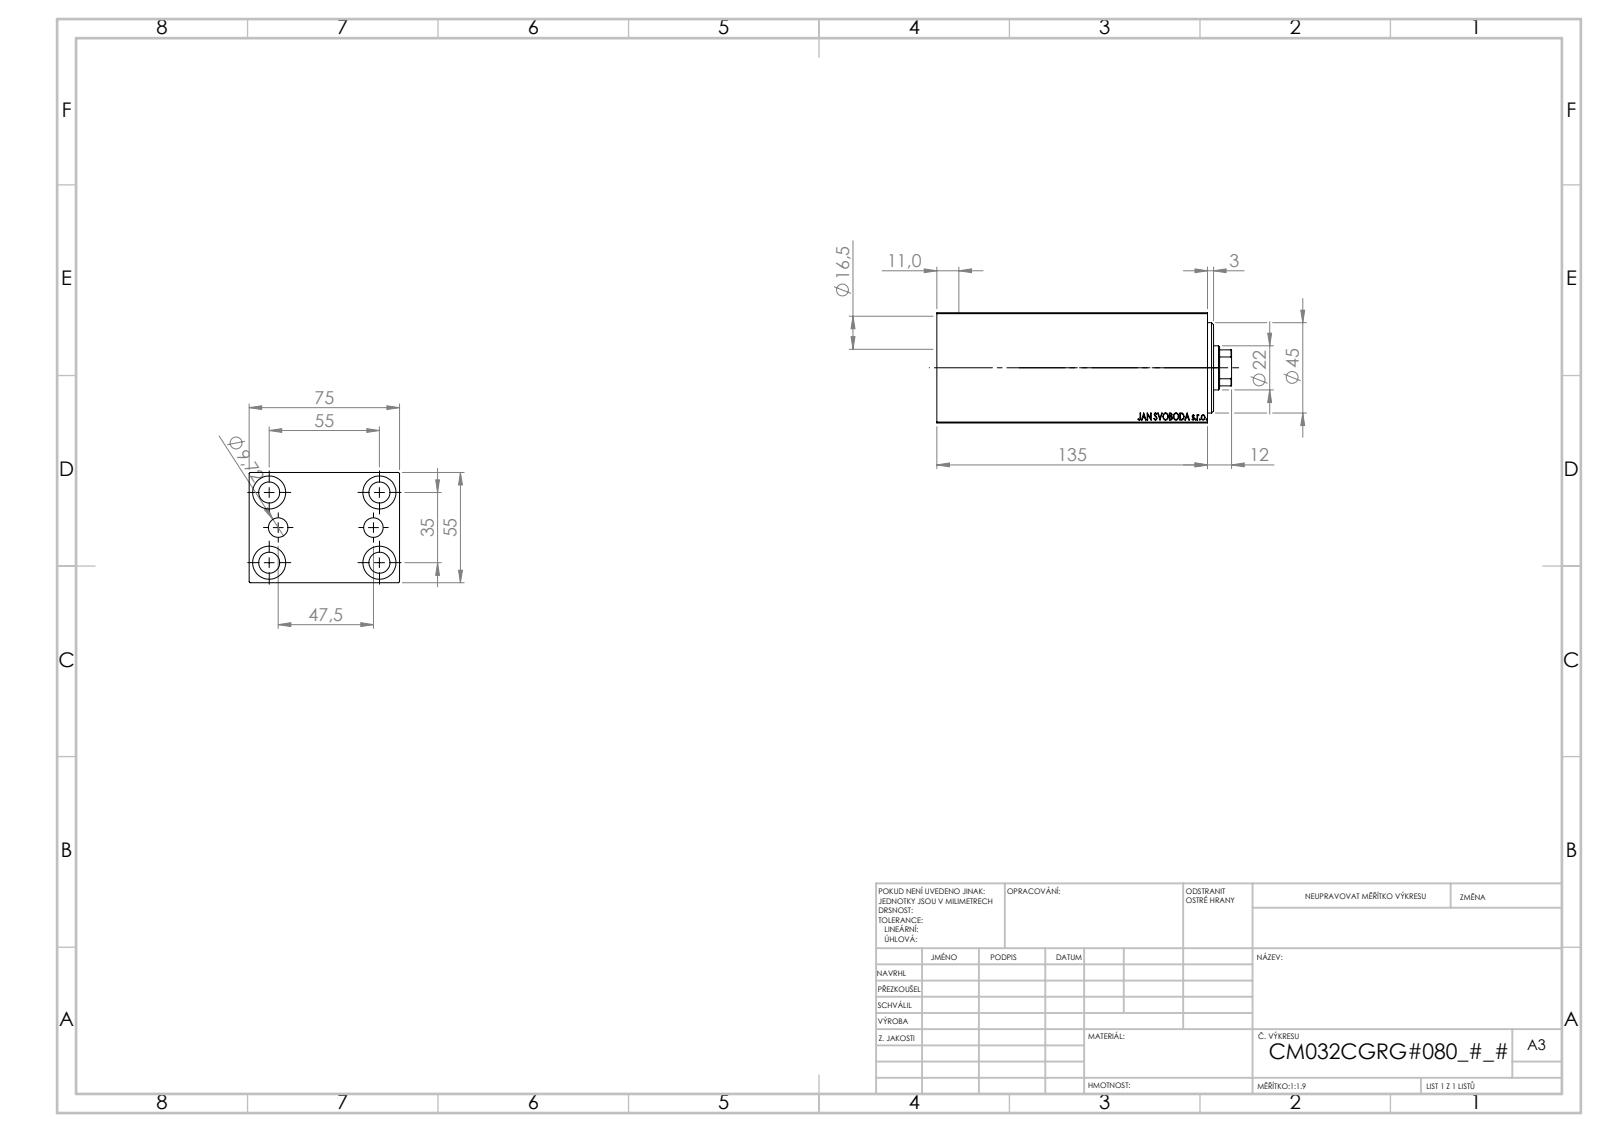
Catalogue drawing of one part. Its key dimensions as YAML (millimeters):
part_name: "V450CM_C_VCP; V450CM_C_Body; V450CM_VC_B"
step_written_by: "SolidWorks 2019 (CONFIG_CONTROL_DESIGN)"
units: millimeters
bodies: {solids: 3, faces: 858, planar: 408, cylindrical: 56, other: 394}
overall_size: [147, 75, 55]
volume: 466216
surface_area: 98269
round_holes:
  - {diameter: 10.5, count: 5}
  - {diameter: 16.5, count: 4}
  - {diameter: 4, count: 2}
  - {diameter: 9.72, count: 2}
  - {diameter: 22, count: 1}
  - {diameter: 25.5, count: 1}
  - {diameter: 32, count: 1}
  - {diameter: 34, count: 1}
  - {diameter: 45, count: 1}
partial_cylinders:
  - {radius: 10.5, count: 1}
face_to_face_distances: [55, 75, 10, 125, 135, 130, 5, 120, 11, 124]
hole_center_spacings: [17.9, 32.6, 54.16, 23.75, 35, 55, 65.19, 47.5]
